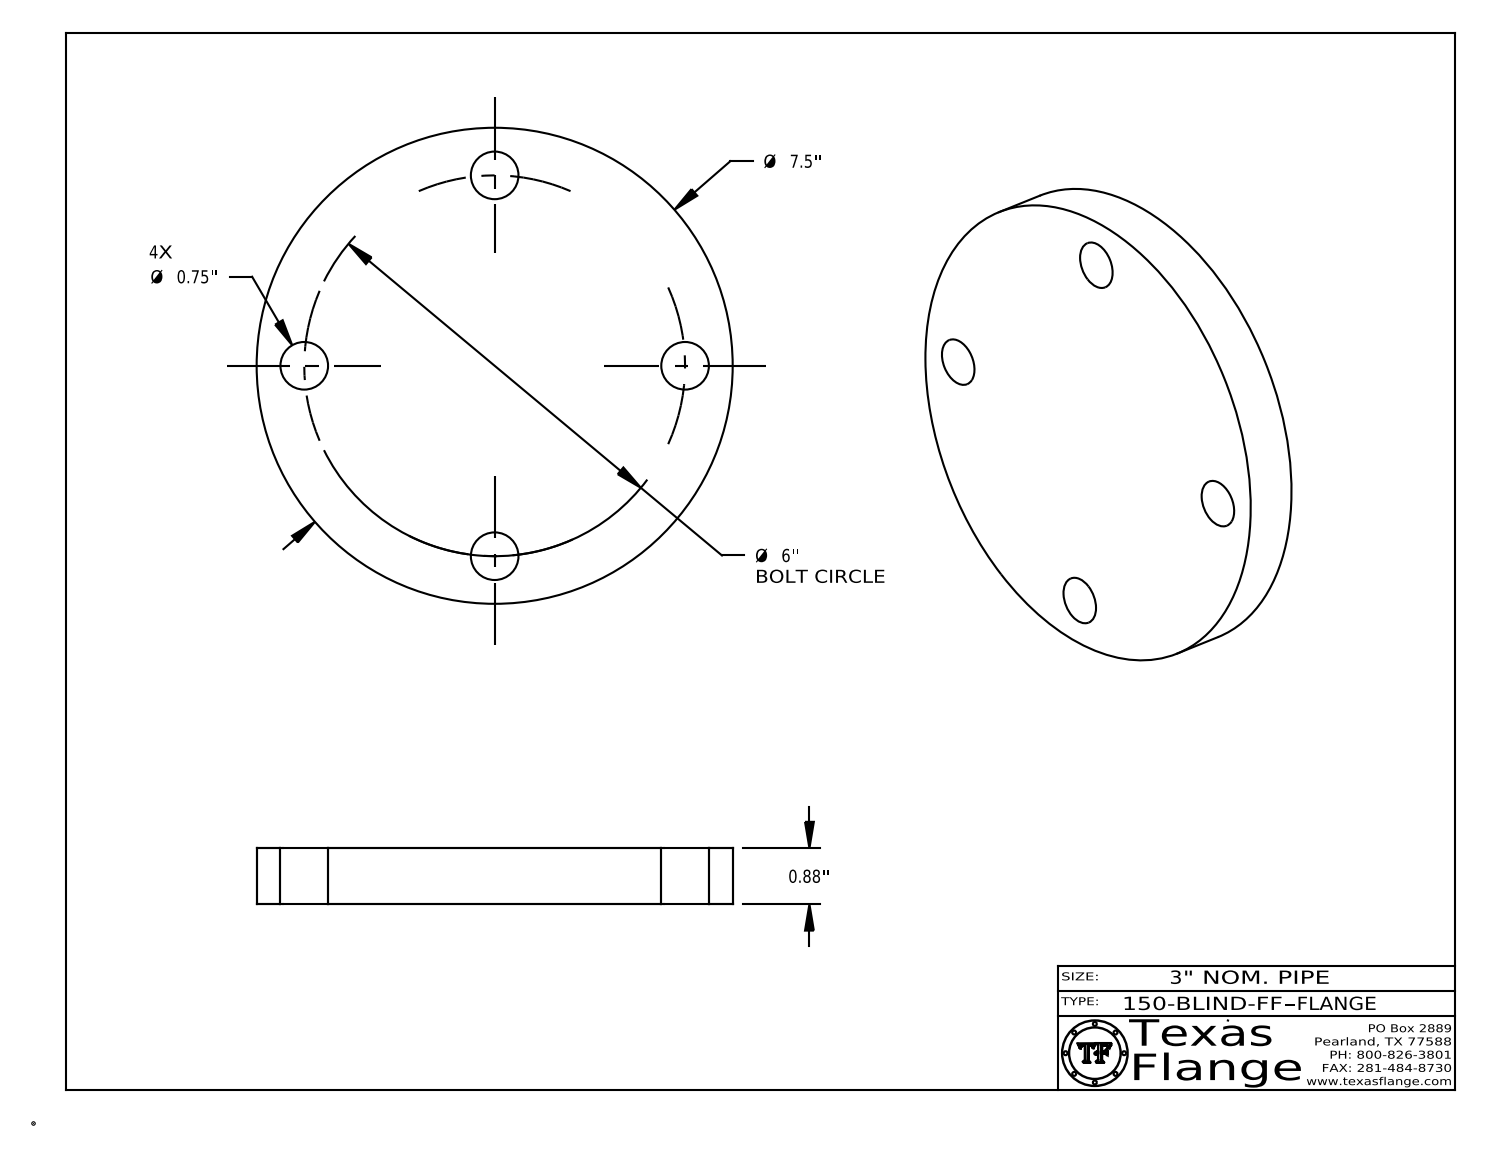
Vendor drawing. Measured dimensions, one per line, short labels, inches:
name: 150-BLIND-FF
written by: CATIA V5 STEP AP214 (AUTOMOTIVE_DESIGN)
unit: in
bodies: 1 solid, 397 faces (367 planar, 30 cylindrical, 0 other)
size: 7.5 × 7.5 × 0.88
volume: 37.32 in³; area: 113.9 in²
holes: 4× ⌀0.75, 1× ⌀0.495
bosses: 8× ⌀0.03, 1× ⌀7.5, 1× ⌀0.39
face distances: 0.88, 0.865, 0.015, 0.148, 0.144, 0.027, 0.122, 0.096, 0.021, 0.101
hole spacings: 4.243, 2.296, 5.543, 6
